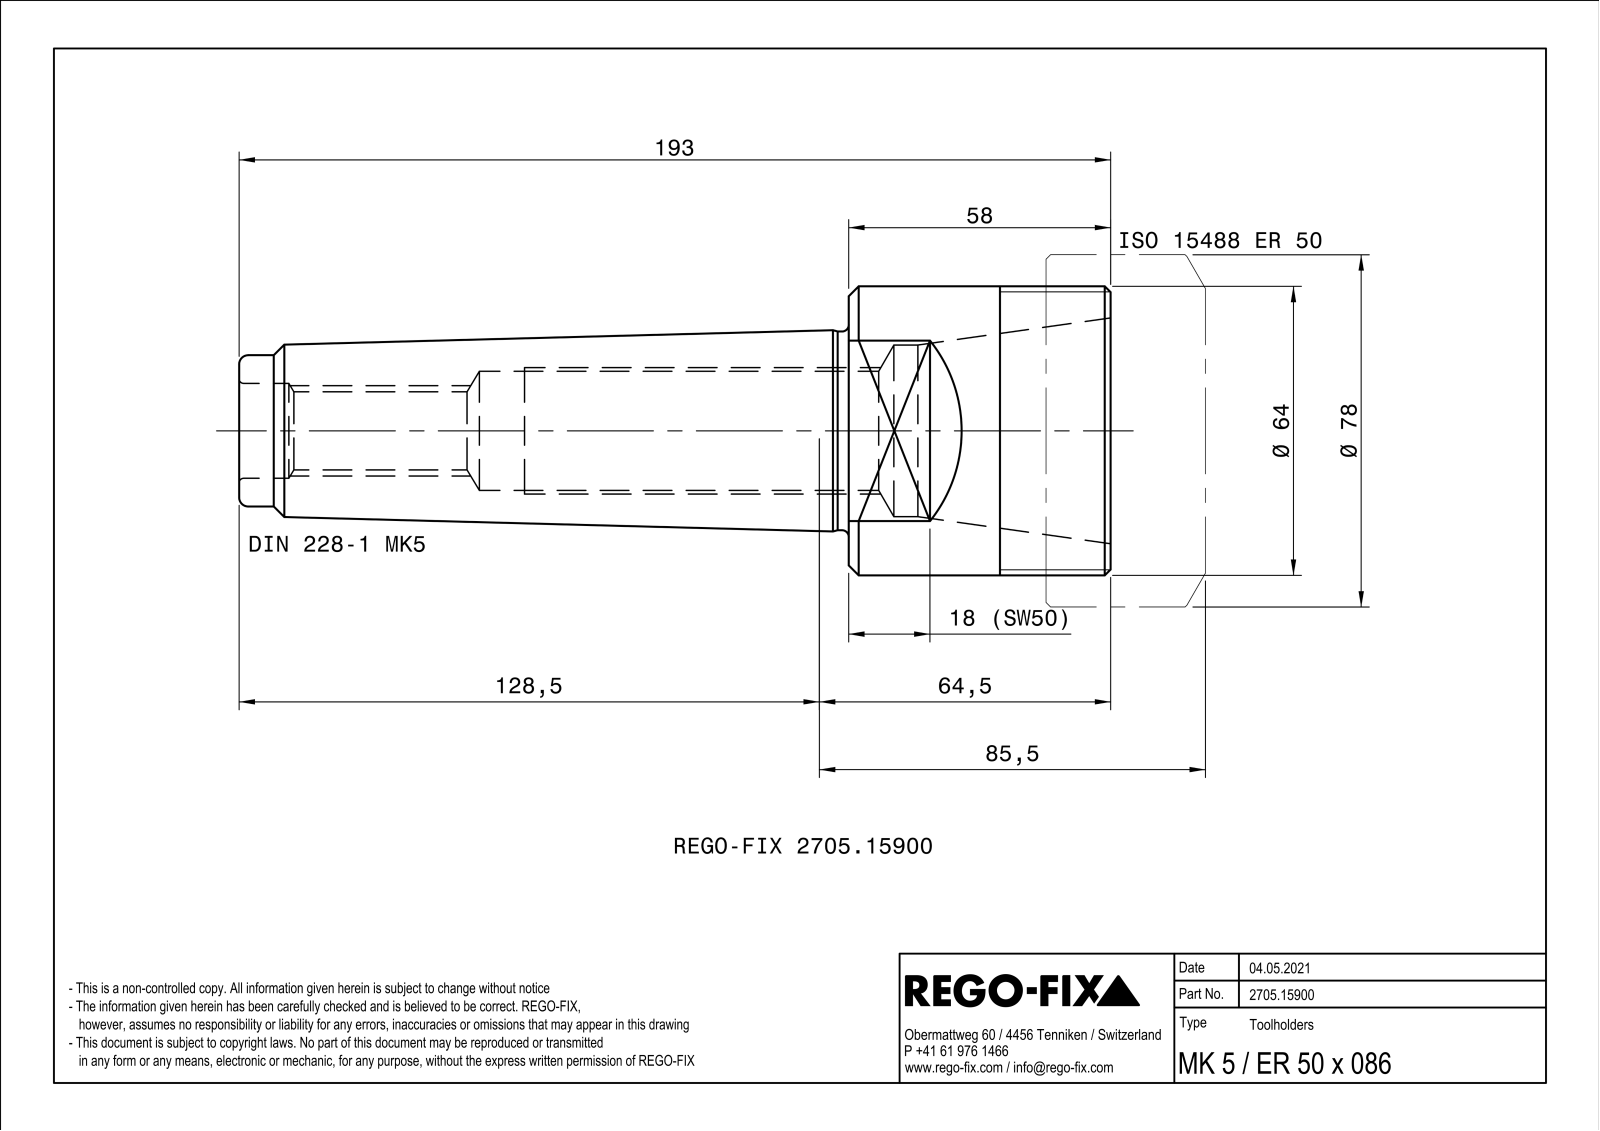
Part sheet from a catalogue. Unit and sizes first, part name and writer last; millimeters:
Units: millimetres
Overall size (bounding box): 193 × 64 × 64
Round holes (diameter × count): ⌀17.29 ×1, ⌀21 ×1, ⌀26.38 ×1, ⌀38 ×1
Round bosses / shafts (diameter × count): ⌀64 ×1, ⌀44 ×1, ⌀33.5 ×1
Main face-to-face distances: 58, 50, 193, 135
Volume: 219 567 mm³ · Surface area: 49 602 mm²
Bodies: 1 solid, 31 faces (7 planar, 10 cylindrical, 14 other)
Part name (STEP PRODUCT): NOCUT
STEP written by: SIEMENS PLM Software Solid Edge ST10 (AUTOMOTIVE_DESIGN)
